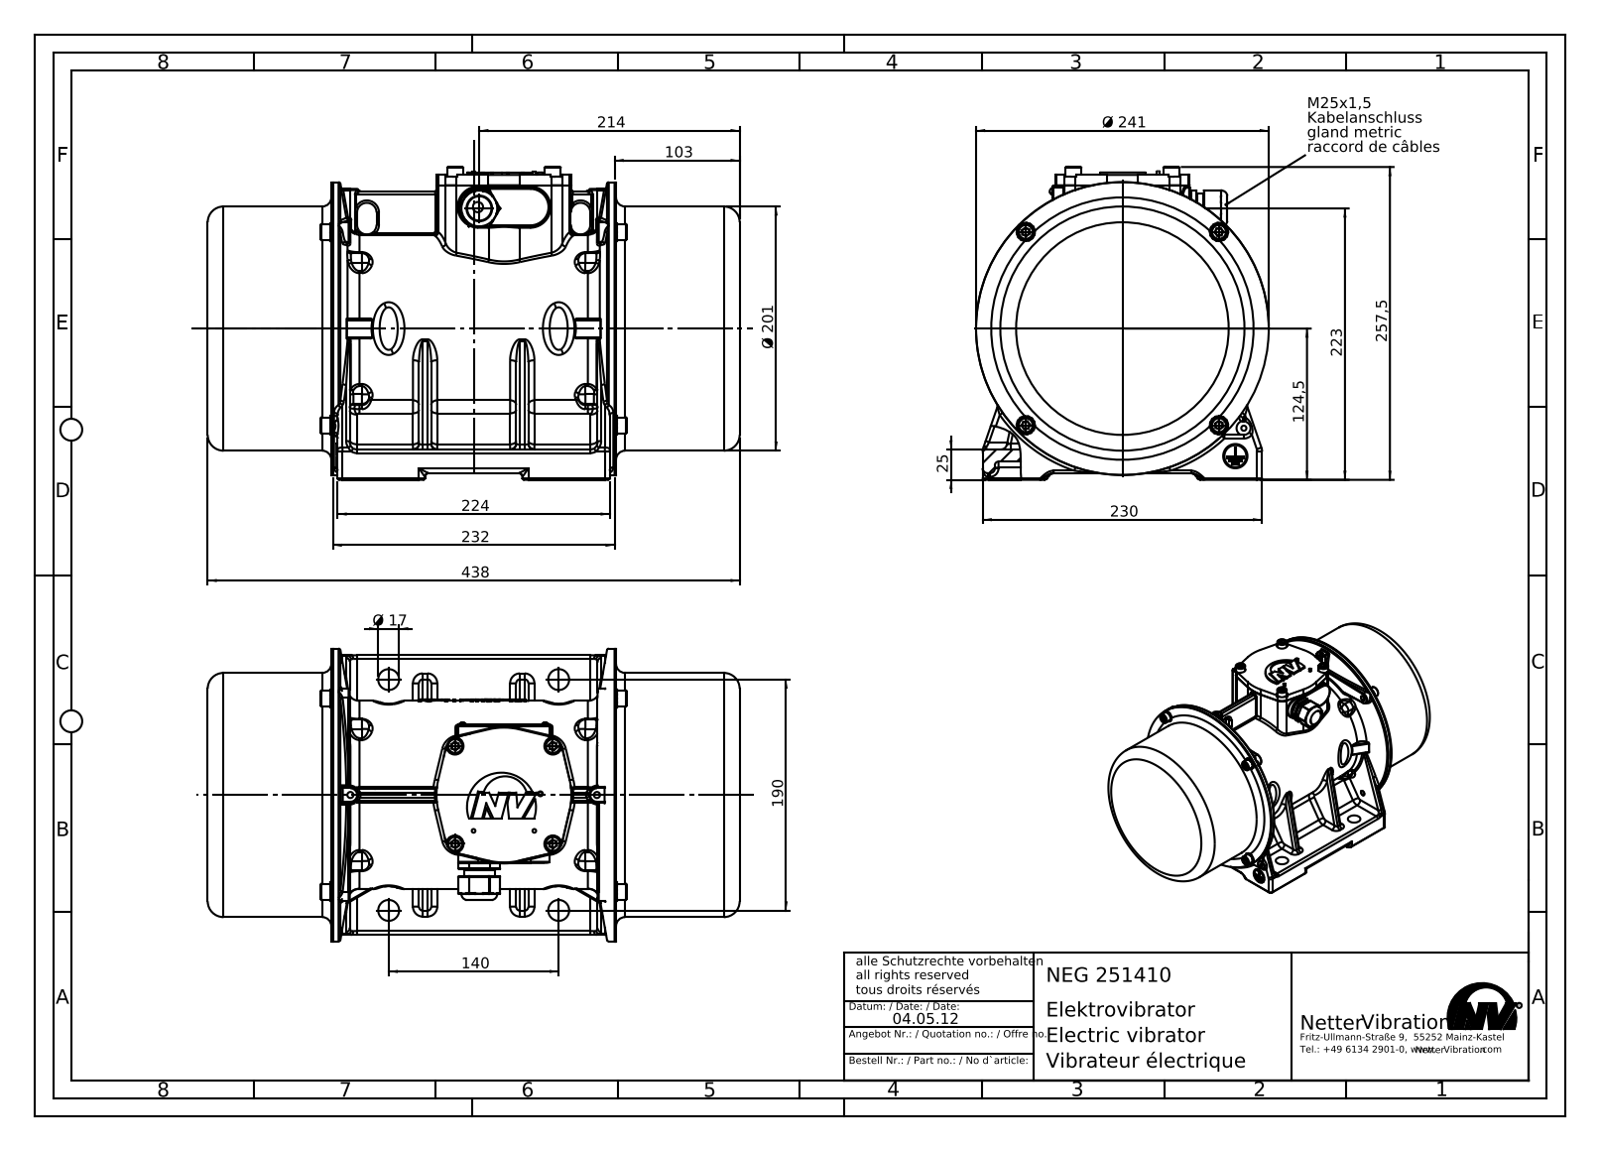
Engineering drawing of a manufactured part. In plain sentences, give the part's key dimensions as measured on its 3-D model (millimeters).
The part is named "NEG 251410". Its 3-D file was written by "SolidWorks 2010 (AUTOMOTIVE_DESIGN)". It is 3 solids with 3220 faces: 1529 planar, 232 cylindrical and 1459 other. Overall it measures 438 by 257.54 by 241 millimeters. Its volume is 6 636 000 cubic millimeters and its surface area 936 114 square millimeters. Round holes: 4 of diameter 3.4, 4 of diameter 3.5, 4 of diameter 6.8, 4 of diameter 8.4, 4 of diameter 9, 4 of diameter 17.2, 1 of diameter 20, 1 of diameter 23.5, 1 of diameter 198.6. Round bosses or shafts: 8 of diameter 13, 4 of diameter 15, 4 of diameter 8, 4 of diameter 3, 1 of diameter 241, 1 of diameter 201, 1 of diameter 25. Partial cylindrical surfaces (rounded edges, fillets, slot ends): 30 of radius 0.5, 8 of radius 2.5, 4 of radius 1, 4 of radius 4. The main face-to-face distances are 1.2, 101.8, 335, 232, 333.8, 103, 436.8, 10, 435.6, 438. The hole center spacings are 112.5, 159.1, 56, 68, 88.09, 140, 190, 225.
